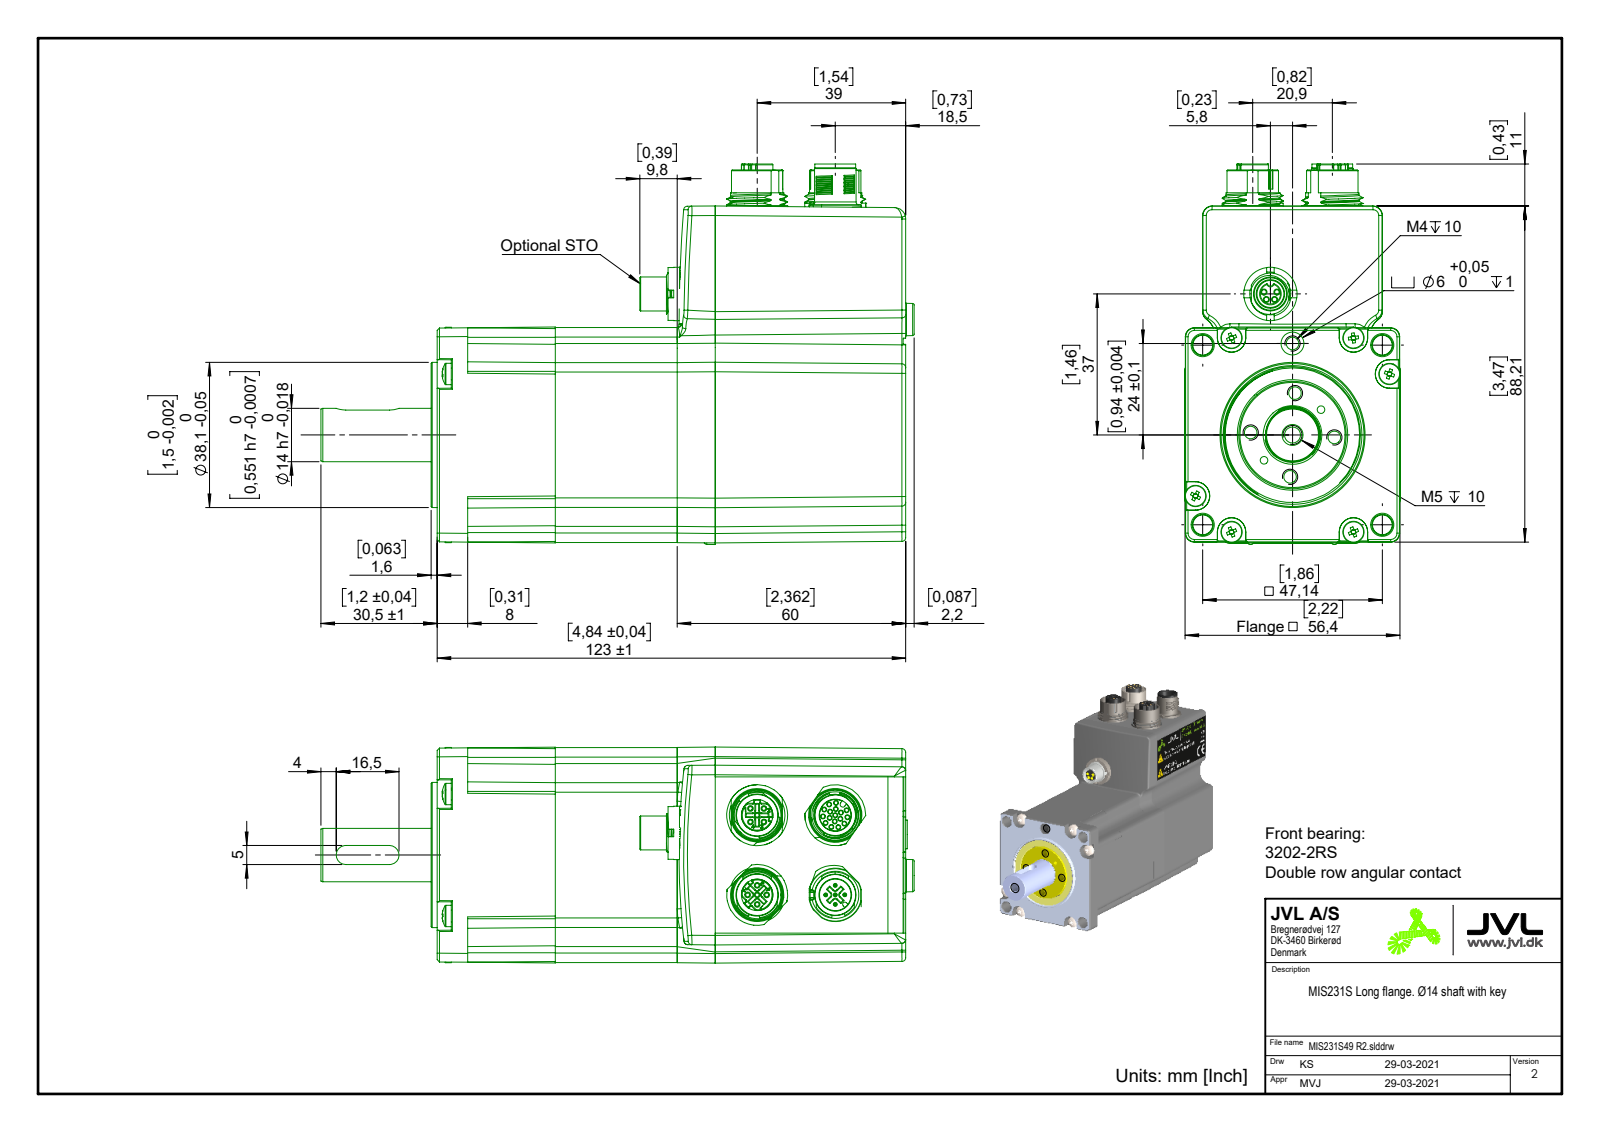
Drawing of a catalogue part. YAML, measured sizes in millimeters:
part_name: "MIS231S49 R2"
step_written_by: "SolidWorks 2020 (AUTOMOTIVE_DESIGN)"
units: millimeters
bodies: {solids: 2, faces: 2144, planar: 906, cylindrical: 546, other: 692}
overall_size: [155.7, 99.83, 56.67]
volume: 446155
surface_area: 53146
round_holes:
  - {diameter: 1, count: 31}
  - {diameter: 3.3, count: 6}
  - {diameter: 1.2, count: 4}
  - {diameter: 12.2, count: 3}
  - {diameter: 2, count: 2}
  - {diameter: 11.13, count: 2}
  - {diameter: 4.2, count: 1}
  - {diameter: 6, count: 1}
  - {diameter: 6.76, count: 1}
  - {diameter: 7.1, count: 1}
  - {diameter: 8.3, count: 1}
  - {diameter: 10.9, count: 1}
round_bosses_or_shafts:
  - {diameter: 5.6, count: 6}
  - {diameter: 3, count: 6}
  - {diameter: 1, count: 5}
  - {diameter: 1.6, count: 4}
  - {diameter: 0.8, count: 4}
  - {diameter: 13.5, count: 3}
  - {diameter: 16, count: 2}
  - {diameter: 14, count: 2}
partial_cylinders:
  - {radius: 0.2, count: 54}
  - {radius: 2.5, count: 31}
  - {radius: 0.1, count: 20}
  - {radius: 0.3, count: 16}
  - {radius: 1, count: 15}
  - {radius: 5, count: 14}
  - {radius: 0.8, count: 13}
  - {radius: 2.3, count: 4}
face_to_face_distances: [57.04, 4.75, 52.29, 56.4, 123, 88.29, 51.92, 0.37, 0.7, 122.3]
hole_center_spacings: [3.54, 1.63, 2.5, 3.25, 1.85, 4.94, 1.64, 2.83]
